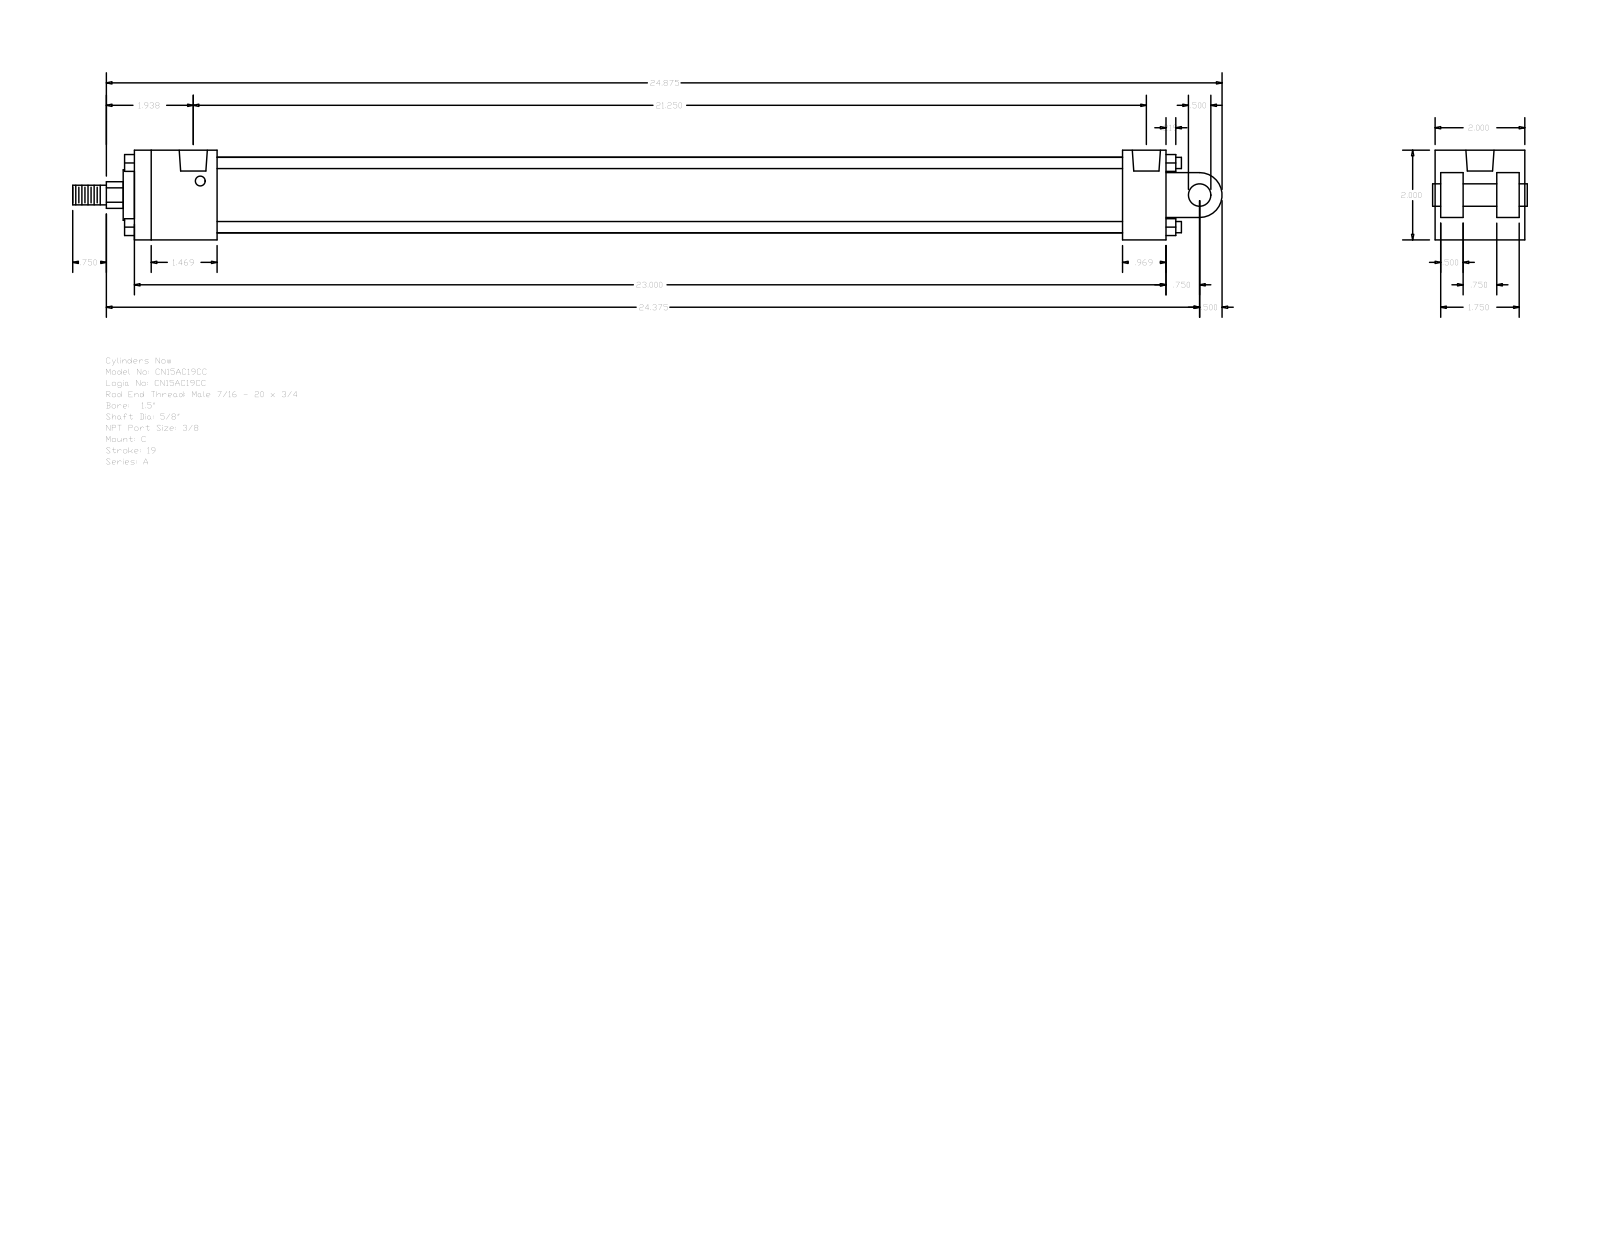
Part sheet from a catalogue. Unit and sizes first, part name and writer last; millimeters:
Units: millimetres
Overall size (bounding box): 650.88 × 50.8 × 50.8
Round holes (diameter × count): ⌀5.56 ×4, ⌀15.93 ×2
Round bosses / shafts (diameter × count): ⌀6.35 ×4, ⌀42.93 ×1, ⌀28.57 ×1, ⌀15.88 ×1, ⌀12.7 ×1, ⌀11.11 ×1
Partial cylindrical surfaces — rounded edges, fillets, slot ends (radius × count): R7.54 ×1, R12.7 ×1
Main face-to-face distances: 50.8, 12.7, 584.2, 34.93, 3.17, 47.63, 15.87, 31.76, 559.59, 24.61
Hole centre spacings: 3.97, 531.81, 535.78, 539.75
Bodies: 0 solids, 135 faces (102 planar, 33 cylindrical, 0 other)
Part name (STEP PRODUCT): A_C__0150_0.625
STEP written by: GSSL Pune (CONFIG_CONTROL_DESIGN)
